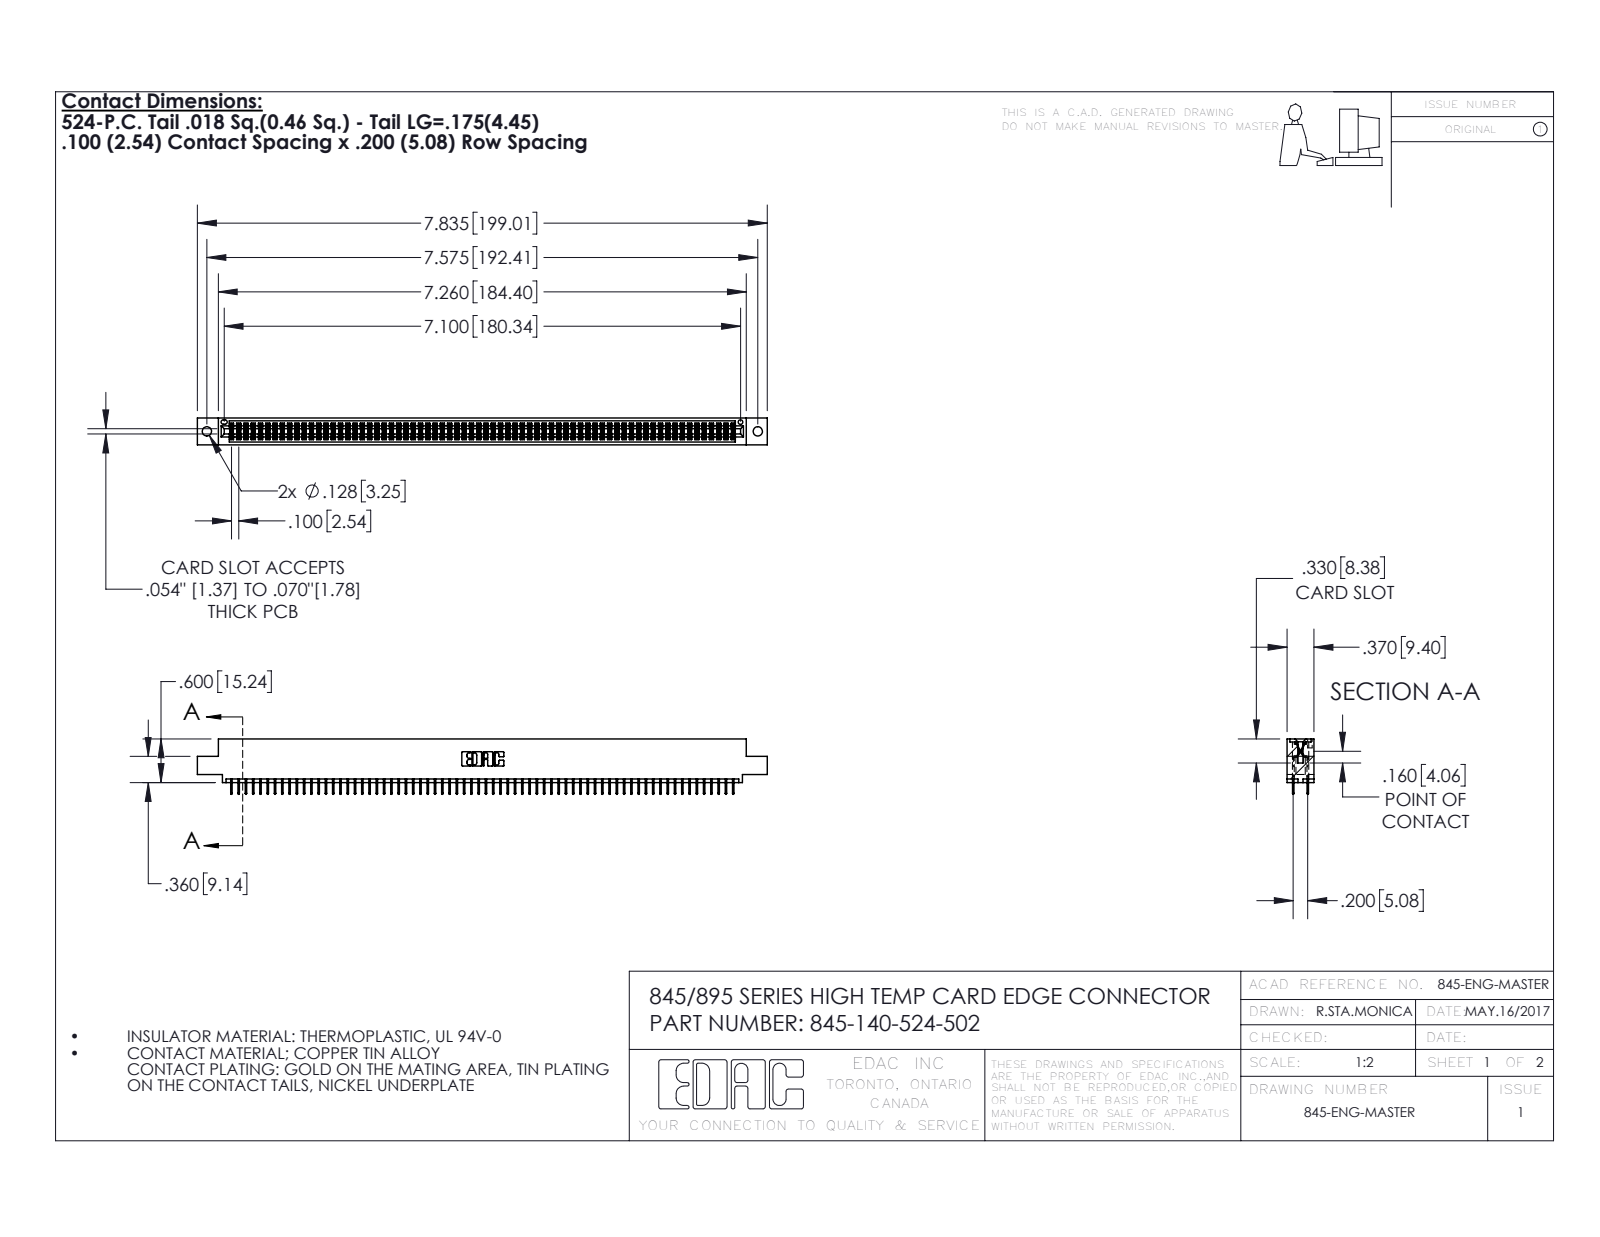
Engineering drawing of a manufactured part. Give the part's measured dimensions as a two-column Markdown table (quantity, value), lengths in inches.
| quantity | value |
| --- | --- |
| part name | 345 Part_0.110 Offset - 0.128 Dia; 345-292-001_345-293-124; 345-140-524-502 |
| STEP written by | SolidWorks 2016 (CONFIG_CONTROL_DESIGN) |
| units | inches |
| bodies | 141 solids, 7690 faces (5544 planar, 2146 cylindrical, 0 other) |
| overall size | 7.835 × 0.762 × 0.37 |
| volume | 1.176 in³ |
| surface area | 43.85 in² |
| round holes (diameter × count) | 0.128 × 2, 0.064 × 1 |
| partial cylindrical surfaces (radius × count) | 0.006 × 210, 0.01 × 22, 0.007 × 6, 0.031 × 6, 0.026 × 3, 0.014 × 2, 0.019 × 2, 0.022 × 2 |
| main face-to-face distances | 0.072, 0.298, 0.2, 0.37, 0.098, 0.272, 0.025, 0.225, 0.072, 0.175 |
| hole center spacings | 0.27, 7.339, 7.575 |
